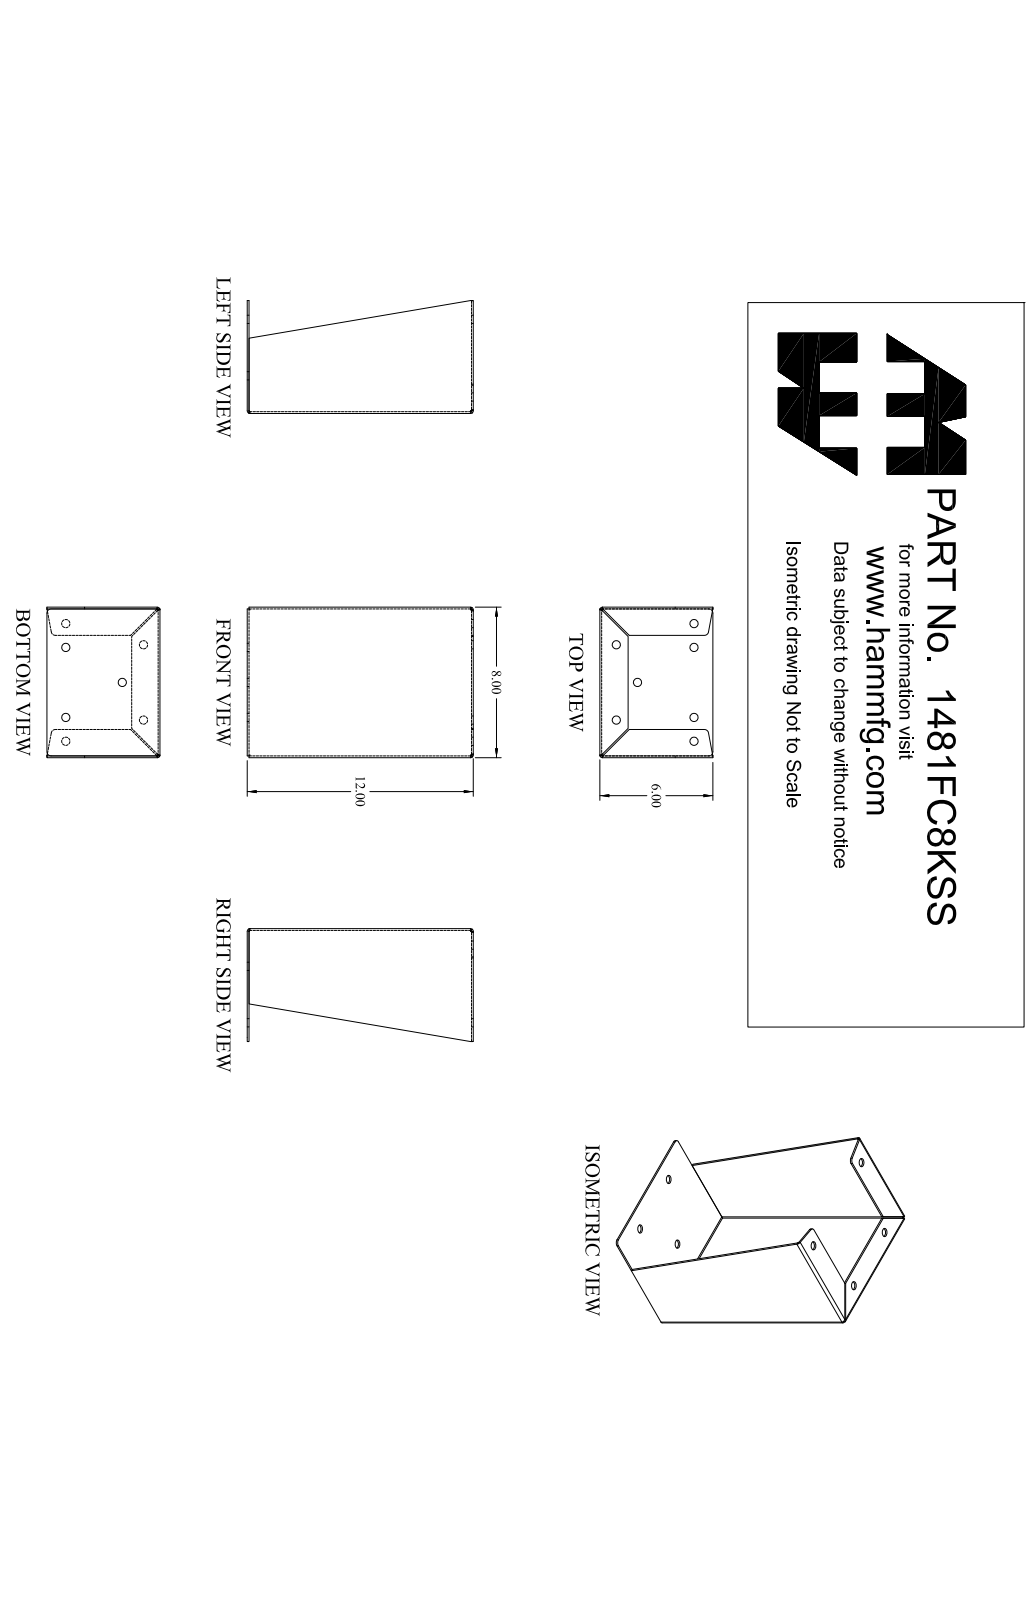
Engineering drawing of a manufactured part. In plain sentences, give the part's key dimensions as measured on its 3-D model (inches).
The part is named "1481FC8KSS_Default". Its 3-D file was written by "SolidWorks 2019 (CONFIG_CONTROL_DESIGN)". It is 1 solid with 78 faces: 42 planar, 30 cylindrical and 6 other. Overall it measures 12 by 8 by 6 inches. Its volume is 26.49 cubic inches and its surface area 565.9 square inches. Round holes: 7 of diameter 0.437. Partial cylindrical surfaces (rounded edges, fillets, slot ends): 6 of radius 0.048, 6 of radius 0.143, 4 of radius 0.22. The main face-to-face distances are 0.095, 7.905, 8, 7.81, 0.095, 11.81, 11.905, 11.905, 12, 1.405. The hole center spacings are 1.266, 2.294, 3.529, 4.127, 4.276, 4.332, 4.984, 5.648.
